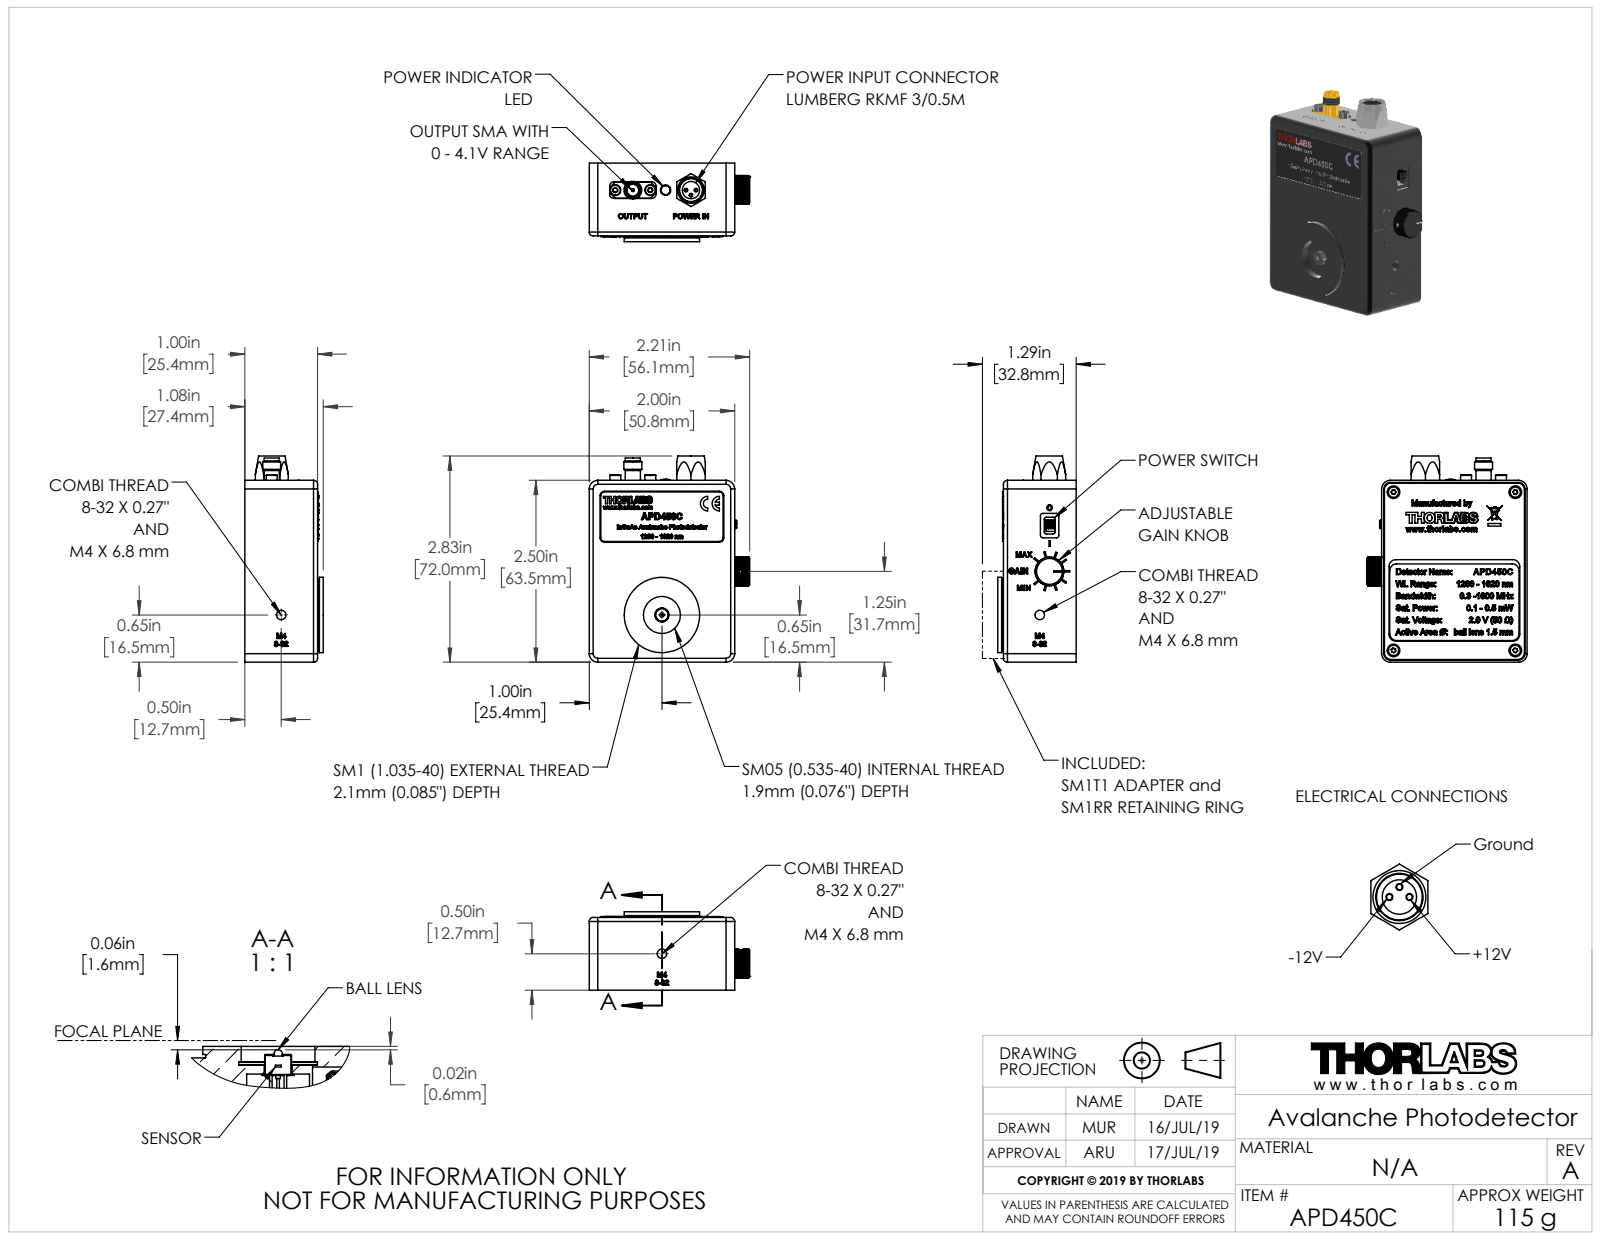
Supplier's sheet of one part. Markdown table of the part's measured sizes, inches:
| quantity | value |
| --- | --- |
| part name | 19.07.02_APD450-Series_Web_Drawing |
| STEP written by | SolidWorks 2018 (CONFIG_CONTROL_DESIGN) |
| units | inches |
| bodies | 0 solids, 5673 faces (3111 planar, 570 cylindrical, 1992 other) |
| overall size | 2.835 × 2.208 × 1.079 |
| round holes (diameter × count) | 0.063 × 12, 0.032 × 6, 0.039 × 5, 0.094 × 4, 0.047 × 3, 0.091 × 2, 0.102 × 2, 0.13 × 2, 0.165 × 2, 0.295 × 2, 0.015 × 1, 0.031 × 1 |
| round bosses / shafts (diameter × count) | 0.079 × 7, 0.062 × 4, 0.15 × 2, 0.065 × 2, 0.063 × 2, 0.051 × 2, 0.018 × 2, 1.035 × 1 |
| partial cylindrical surfaces (radius × count) | 0.012 × 53, 0.006 × 24, 0.016 × 24, 0.098 × 22, 0.039 × 14, 0.031 × 10, 0.13 × 10, 0.059 × 8 |
| main face-to-face distances | 0.062, 0.937, 0.999, 0.063, 0.098, 0.936, 0.874, 1.902, 2, 2.5 |
| hole center spacings | 0.1, 0.969, 0.648, 2.579, 0.069, 0.174, 0.2, 0.64 |
